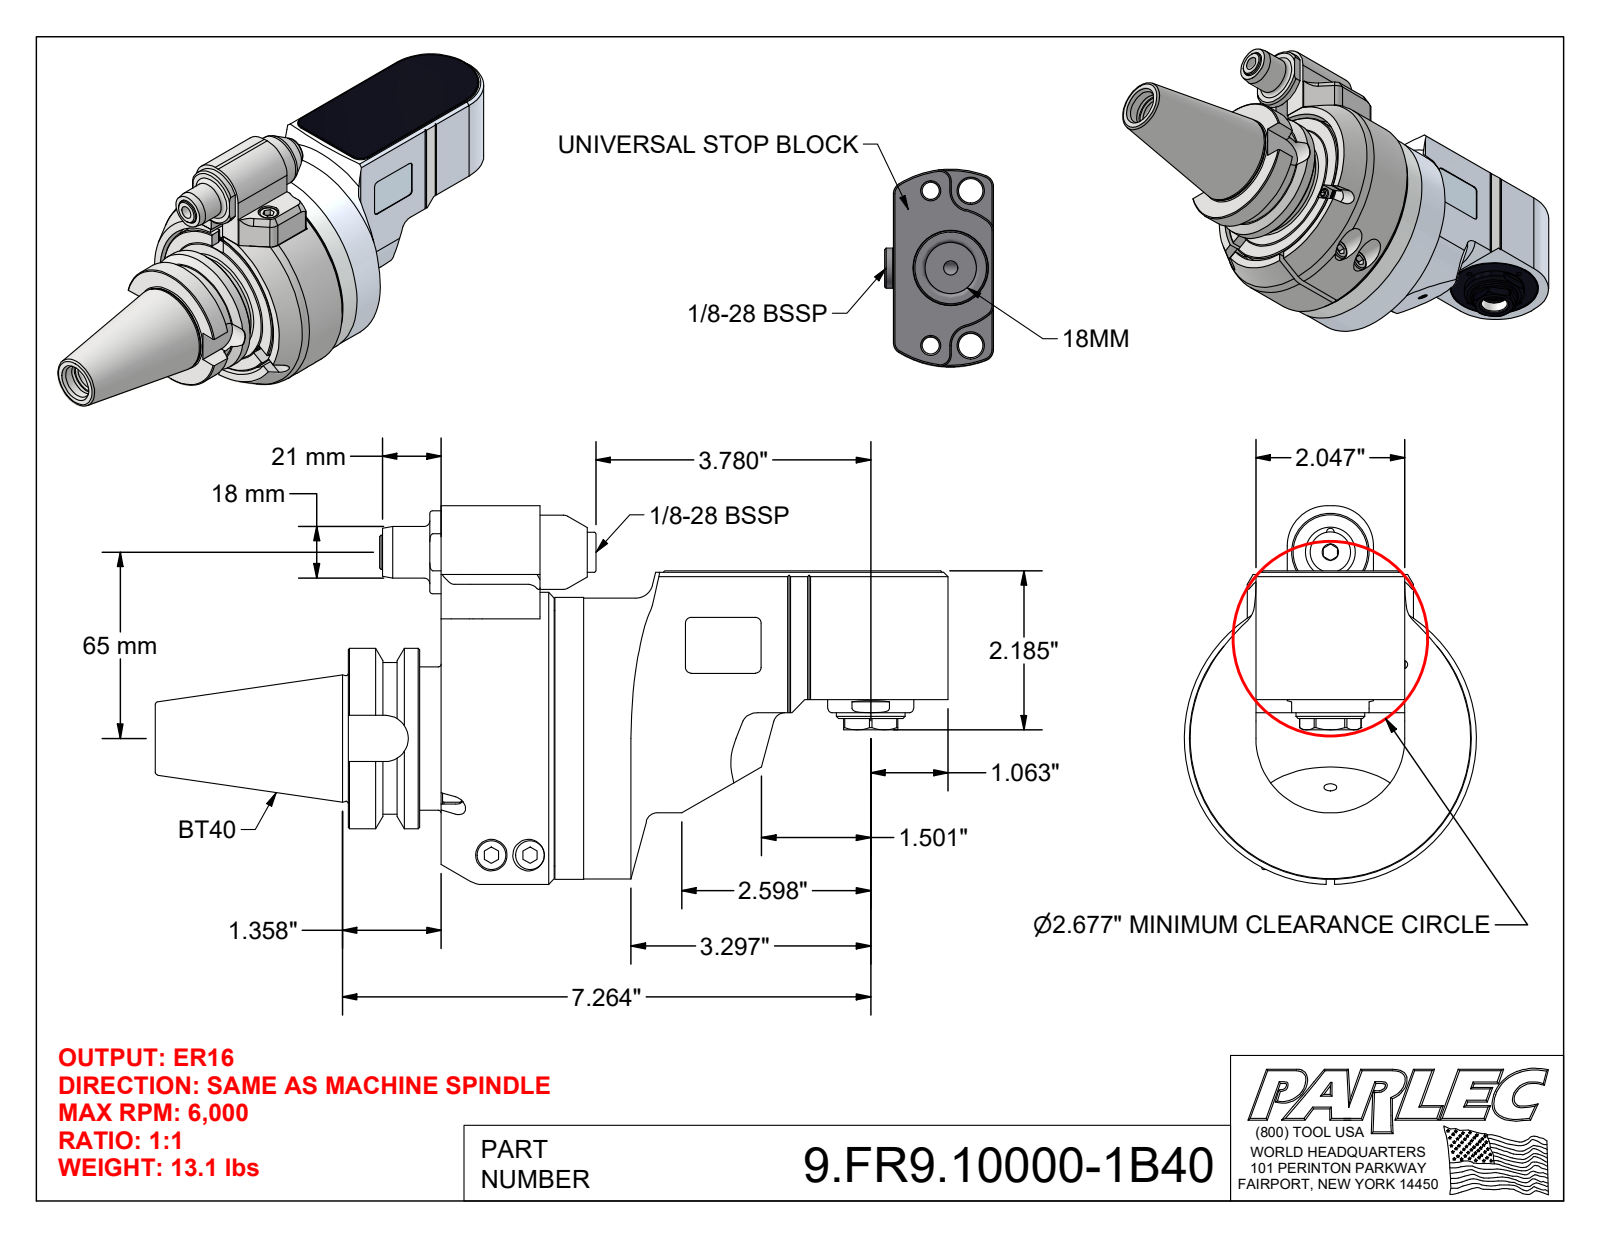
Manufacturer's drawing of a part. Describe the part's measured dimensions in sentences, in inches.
The part is named "9.FR9.10000-1B40; 9_GA1_346_2 (Type 1, BT40, 65mm); 9_FR9_10000". Its 3-D file was written by "Autodesk Inventor 2022 (AUTOMOTIVE_DESIGN)". It is 5 solids with 596 faces: 262 planar, 165 cylindrical and 169 other. Overall it measures 10.902 by 5.206 by 4.016 inches. Its volume is 59.82 cubic inches and its surface area 251.9 square inches. Round holes: 22 of diameter 0.335, 10 of diameter 0.102, 7 of diameter 0.197, 3 of diameter 0.118, 3 of diameter 0.433, 2 of diameter 0.165, 2 of diameter 0.409, 2 of diameter 0.512, 1 of diameter 0.098, 1 of diameter 0.13, 1 of diameter 0.177, 1 of diameter 0.256. Round bosses or shafts: 4 of diameter 0.394, 4 of diameter 0.236, 2 of diameter 0.709, 2 of diameter 0.315, 2 of diameter 0.098, 1 of diameter 4.016, 1 of diameter 3.874, 1 of diameter 3.858. Partial cylindrical surfaces (rounded edges, fillets, slot ends): 12 of radius 0.079, 4 of radius 0.157, 2 of radius 0.02, 2 of radius 0.039, 2 of radius 0.138, 2 of radius 0.197, 2 of radius 0.551, 2 of radius 0.984. The main face-to-face distances are 1.555, 0.295, 1.26, 0.659, 0.335, 2.047, 0.039, 0.02, 1.22, 1.083. The hole center spacings are 1.496, 0.339, 2.973, 0.365, 0.382, 0.435, 0.689, 0.974.
